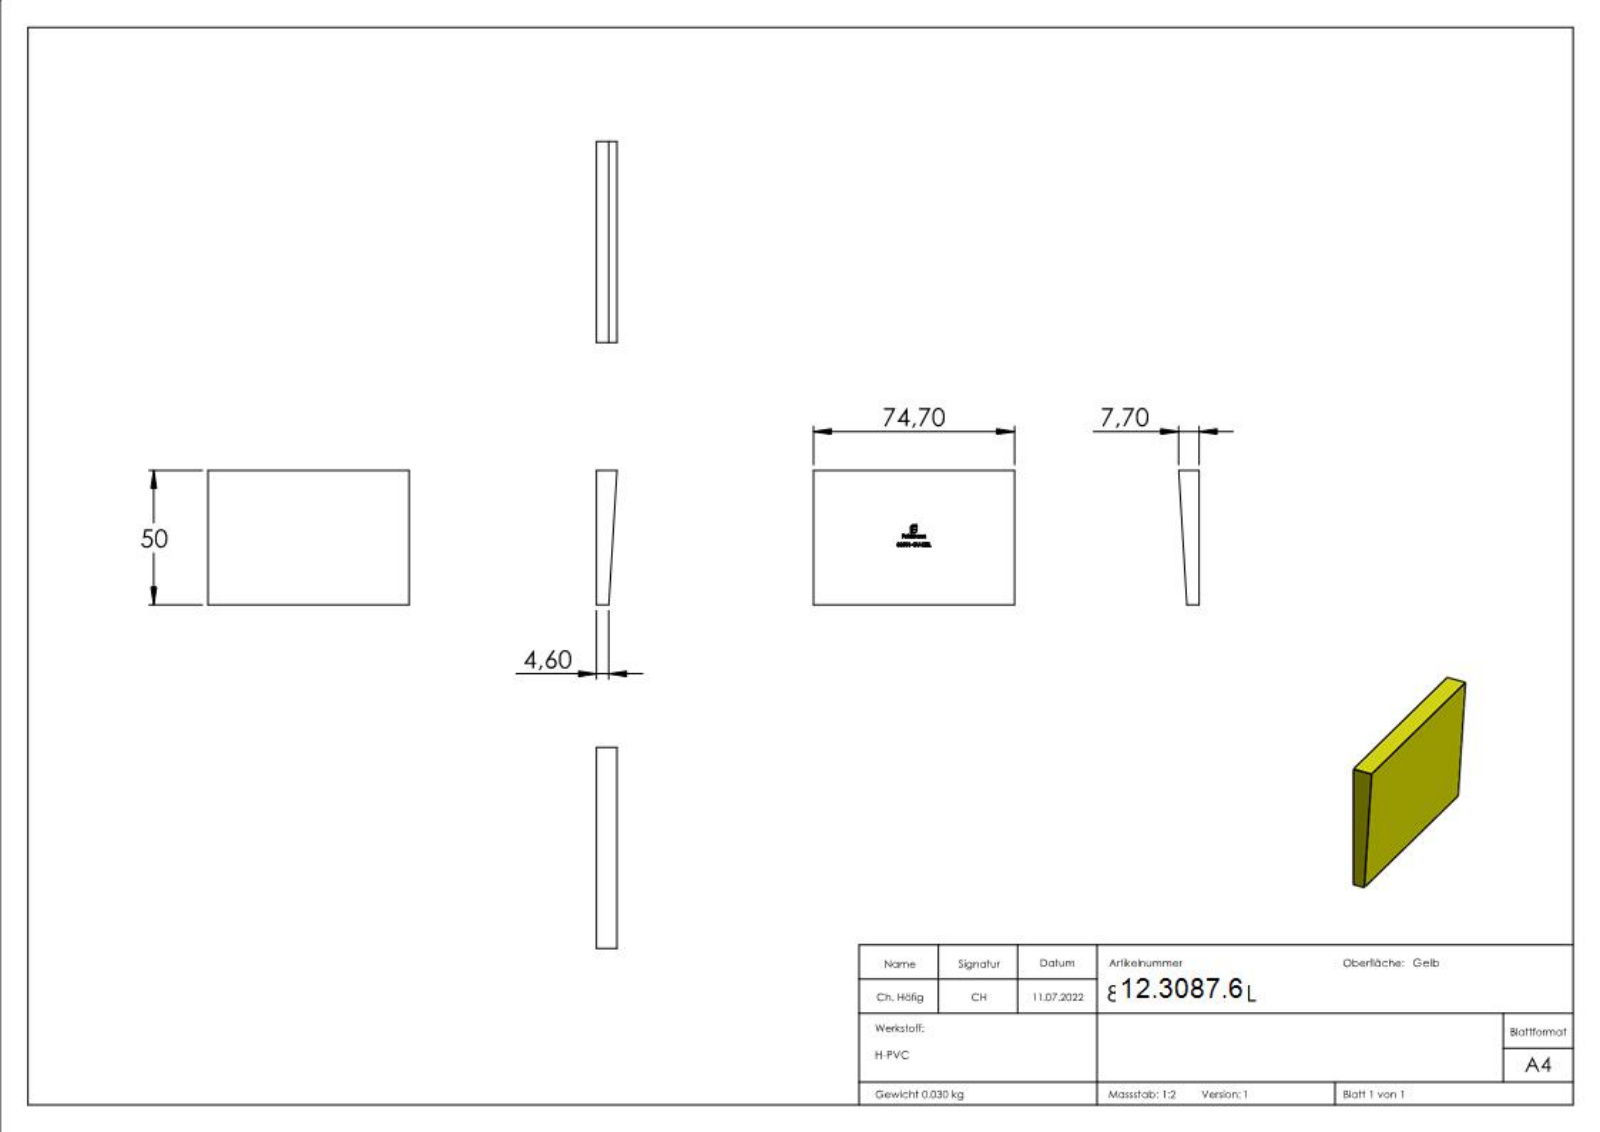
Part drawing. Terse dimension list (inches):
name: 80501-GU-KEIL
written by: SolidWorks 2018 (CONFIG_CONTROL_DESIGN)
unit: in
bodies: 1 solid, 301 faces (174 planar, 0 cylindrical, 127 other)
size: 2.941 × 1.969 × 0.303
volume: 1.402 in³; area: 13.99 in²
face distances: 1.969, 2.941, 0.013, 0.023, 0.035, 0.241, 0.122, 0.984, 0.08, 1.431
